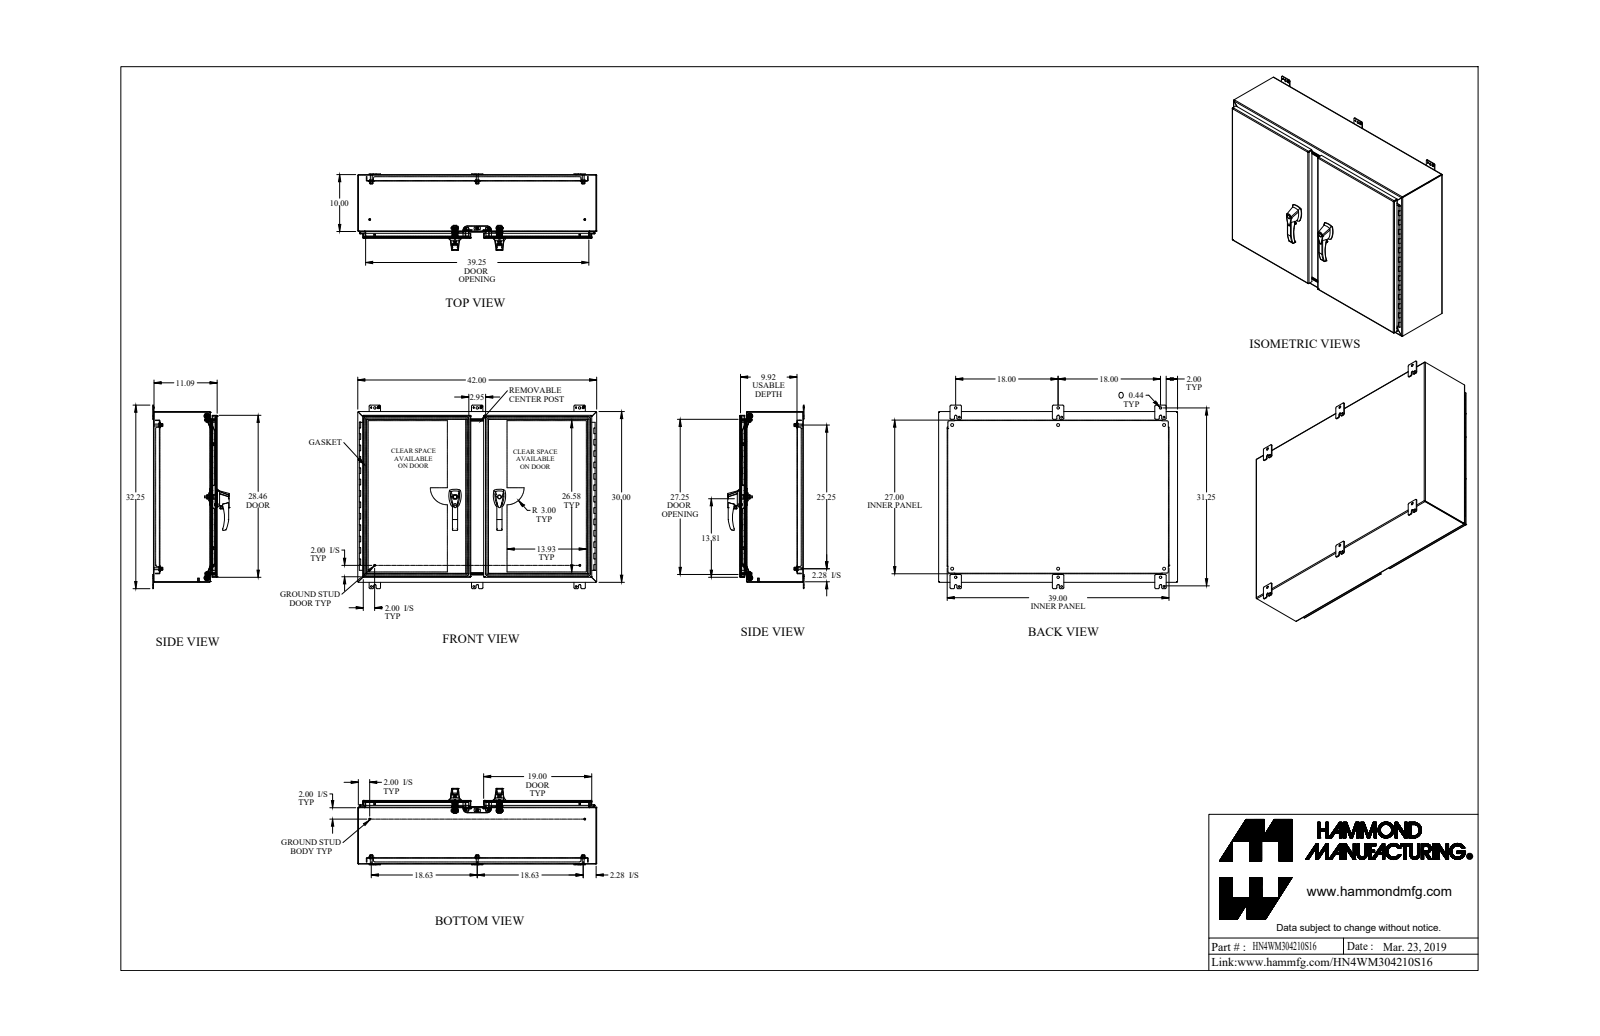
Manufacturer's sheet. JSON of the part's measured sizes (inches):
{"part_name": "HN4WM304210S16", "step_written_by": "SolidWorks 2018 (AUTOMOTIVE_DESIGN)", "units": "inches", "bodies": {"solids": 112, "faces": 2796, "planar": 1313, "cylindrical": 1203, "other": 280}, "overall_size": [42, 32.25, 13.425], "volume_in3": 597.2, "surface_area_in2": 12456, "round_holes": [[0.304, 10], [0.313, 9], [0.25, 8], [0.201, 6], [0.307, 6], [0.445, 6], [0.5, 6], [0.281, 4], [0.313, 4], [0.39, 4], [0.437, 3], [0.11, 2]], "round_bosses_or_shafts": [[1, 8], [0.65, 6], [0.375, 6], [0.332, 6], [0.293, 6], [0.75, 4], [0.625, 4], [0.44, 4]], "partial_cylinders_radius": [[0.125, 37], [0.25, 34], [0.018, 32], [0.188, 26], [0.06, 22], [0.5, 22], [0.048, 19], [0.143, 19]], "face_to_face_distances": [0.095, 1.032, 11.09, 10.995, 0.095, 11.185, 11.09, 9.963, 1.127, 10.058], "hole_center_spacings": [31.376, 6, 40.566, 18.625, 12, 25.25, 37.25, 41.876]}
